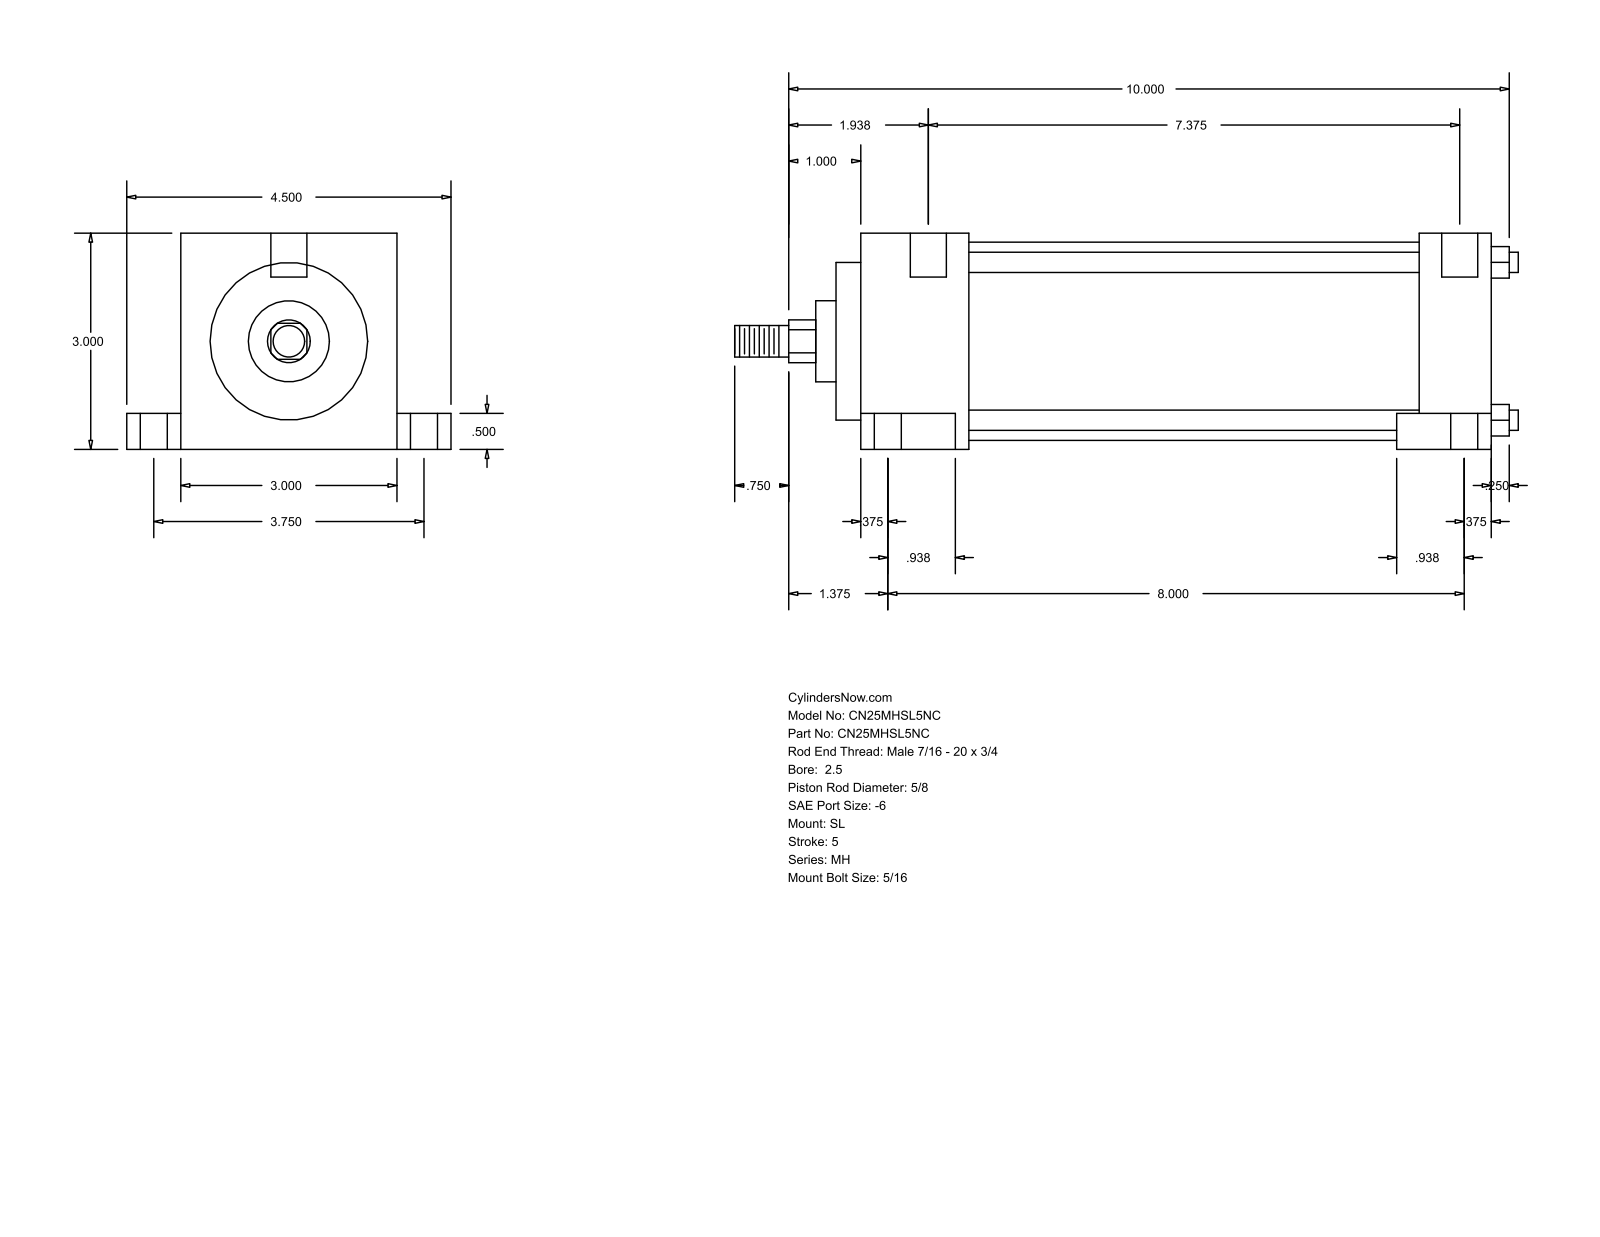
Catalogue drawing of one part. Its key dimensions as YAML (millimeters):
part_name: "MH_SL__0250_0.625"
step_written_by: "GSSL Pune (CONFIG_CONTROL_DESIGN)"
units: millimeters
bodies: {solids: 0, faces: 86, planar: 61, cylindrical: 25, other: 0}
overall_size: [276.23, 114.3, 76.2]
round_holes:
  - {diameter: 5.56, count: 2}
  - {diameter: 9.53, count: 2}
  - {diameter: 15.88, count: 2}
  - {diameter: 12.7, count: 1}
round_bosses_or_shafts:
  - {diameter: 7.14, count: 4}
  - {diameter: 69.85, count: 1}
  - {diameter: 55.55, count: 1}
  - {diameter: 28.57, count: 1}
  - {diameter: 15.88, count: 1}
  - {diameter: 11.11, count: 1}
partial_cylinders:
  - {radius: 7.54, count: 1}
face_to_face_distances: [76.2, 25.4, 205.58, 230.98, 63.5, 12.7, 19.05, 95.25, 31.75, 197.64]
hole_center_spacings: [47.65, 3.17, 95.24]
